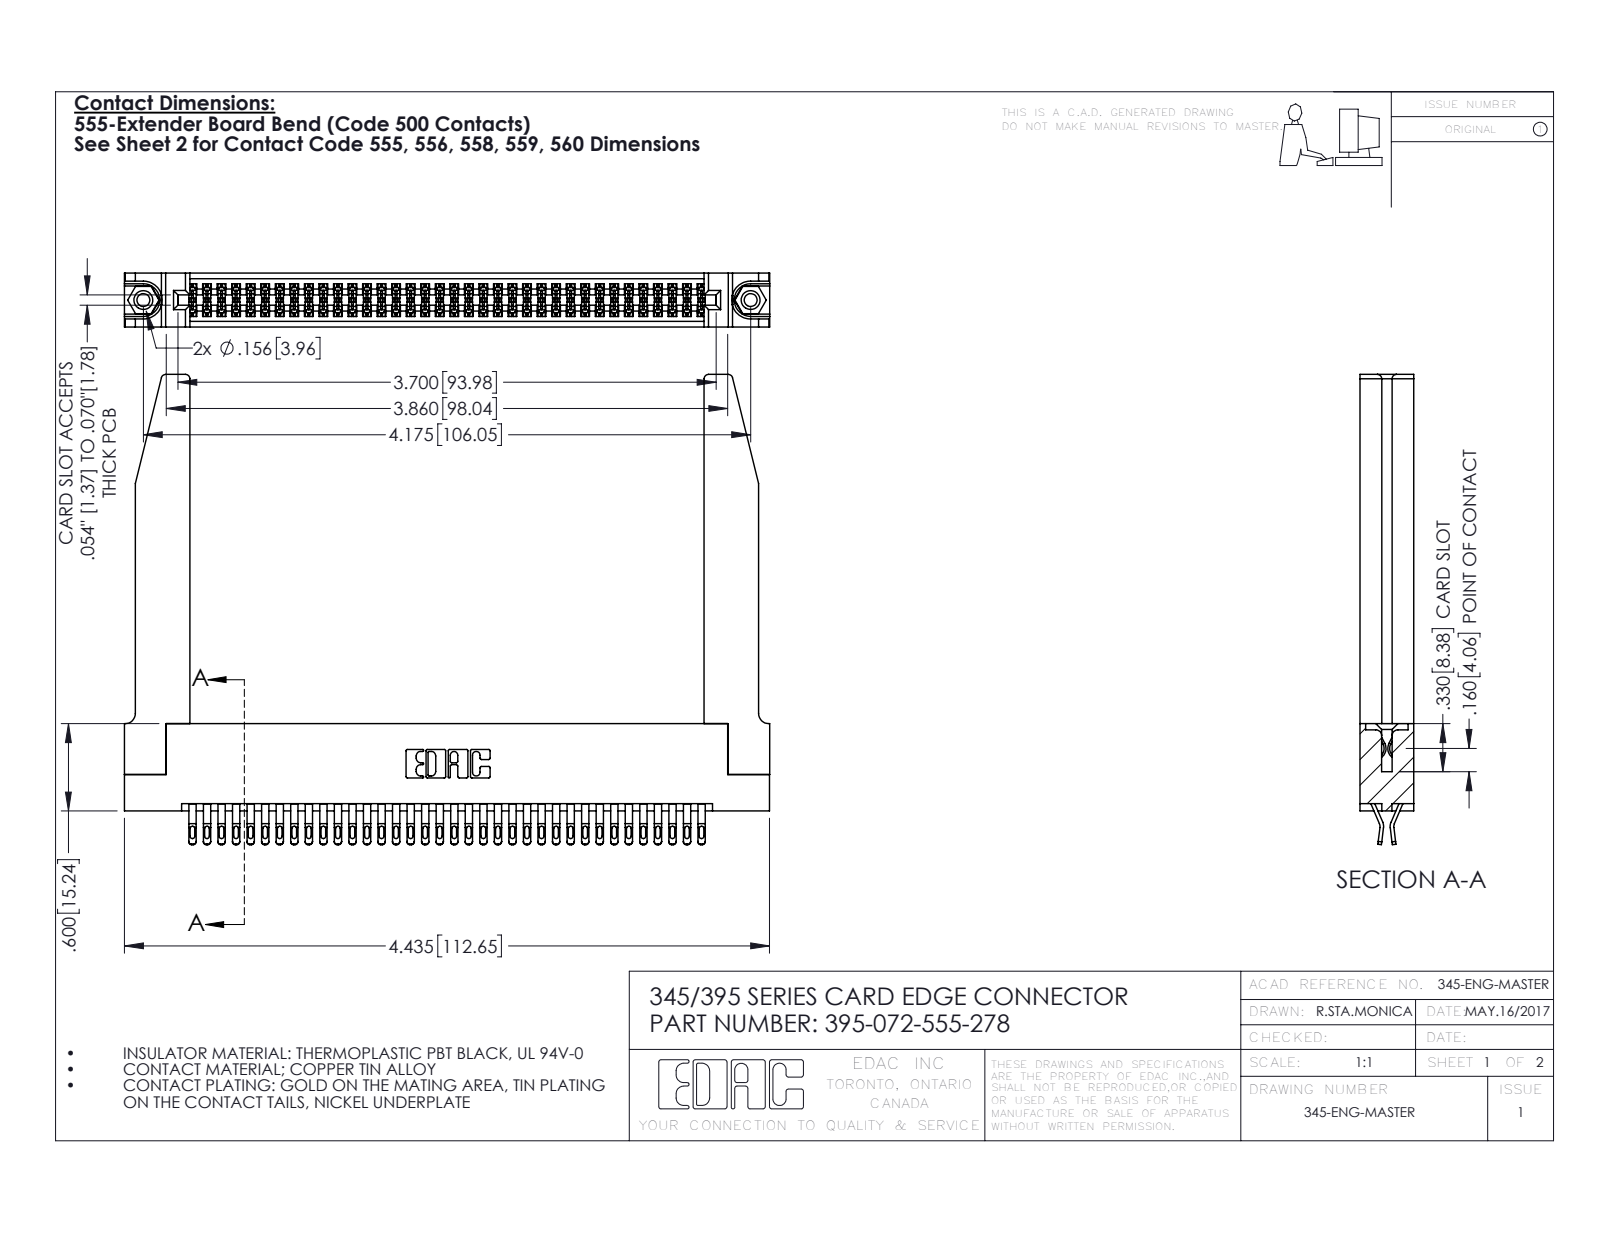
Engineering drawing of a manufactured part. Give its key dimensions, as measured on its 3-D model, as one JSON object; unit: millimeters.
{"part_name": "345-220-078_345-220-078; 345-250-001_345-250-001-102; 345 Part_Flush Mounting Lugs - 0.156 Dia-TH; 345-292-001_555 Tail (+1 more)", "step_written_by": "SolidWorks 2016 (CONFIG_CONTROL_DESIGN)", "units": "millimeters", "bodies": {"solids": 77, "faces": 4392, "planar": 2454, "cylindrical": 1886, "other": 52}, "overall_size": [112.7, 82.1, 9.4], "volume_mm3": 18860, "surface_area_mm2": 23850, "round_holes": [[2.3, 2], [3.2, 2], [4, 2], [1.6, 1]], "round_bosses_or_shafts": [[3.9, 2]], "partial_cylinders_radius": [[0.4, 180], [0.5, 144], [0.2, 108], [0.3, 22], [0.8, 8], [0.2, 6], [0.8, 6], [0.7, 3]], "face_to_face_distances": [9.4, 1.8, 7.6, 5.1, 0.6, 2.5, 6.9, 5.7, 3.8, 3.8], "hole_center_spacings": [6.9, 100.1, 106]}
